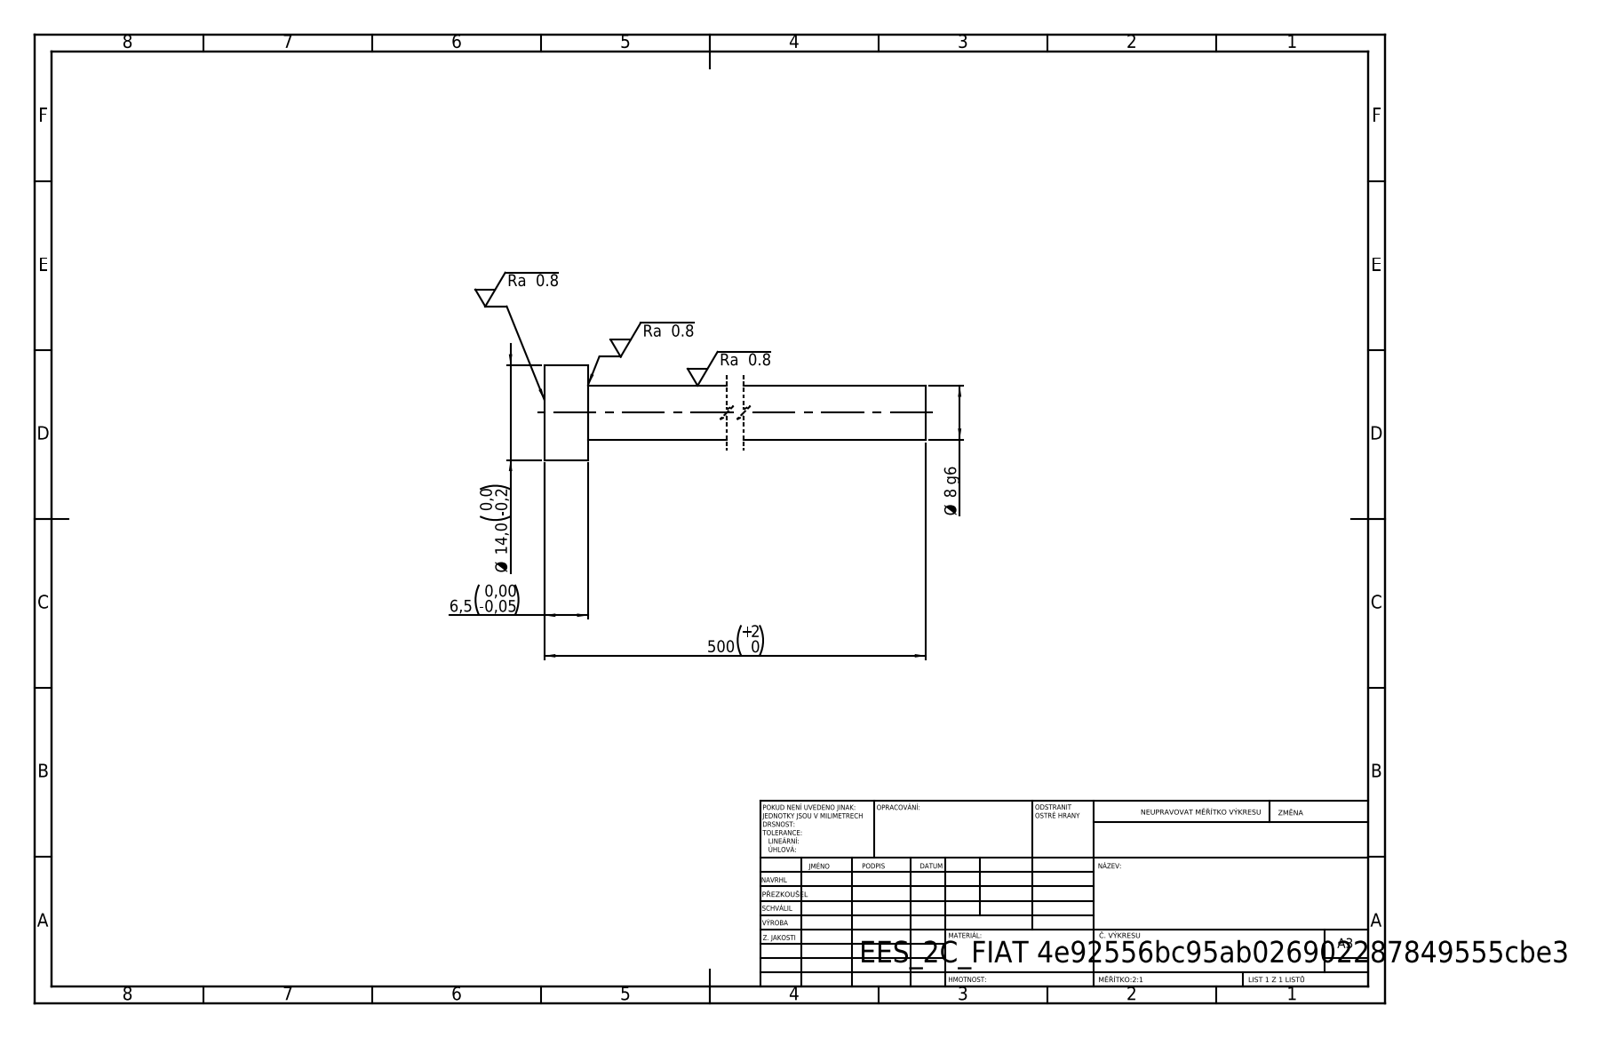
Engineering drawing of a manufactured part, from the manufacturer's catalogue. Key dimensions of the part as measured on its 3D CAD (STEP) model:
STEP written by: SolidWorks 2019 (CONFIG_CONTROL_DESIGN)
Units: millimetres
Bodies: 1 solid, 7 faces (3 planar, 4 cylindrical, 0 other)
Overall size (bounding box): 500 × 14 × 14
Volume: 25 807 mm³ · Surface area: 12 997 mm²
Round bosses / shafts (diameter × count): ⌀14 ×1, ⌀8 ×1
Main face-to-face distances: 6.5, 500, 493.5
